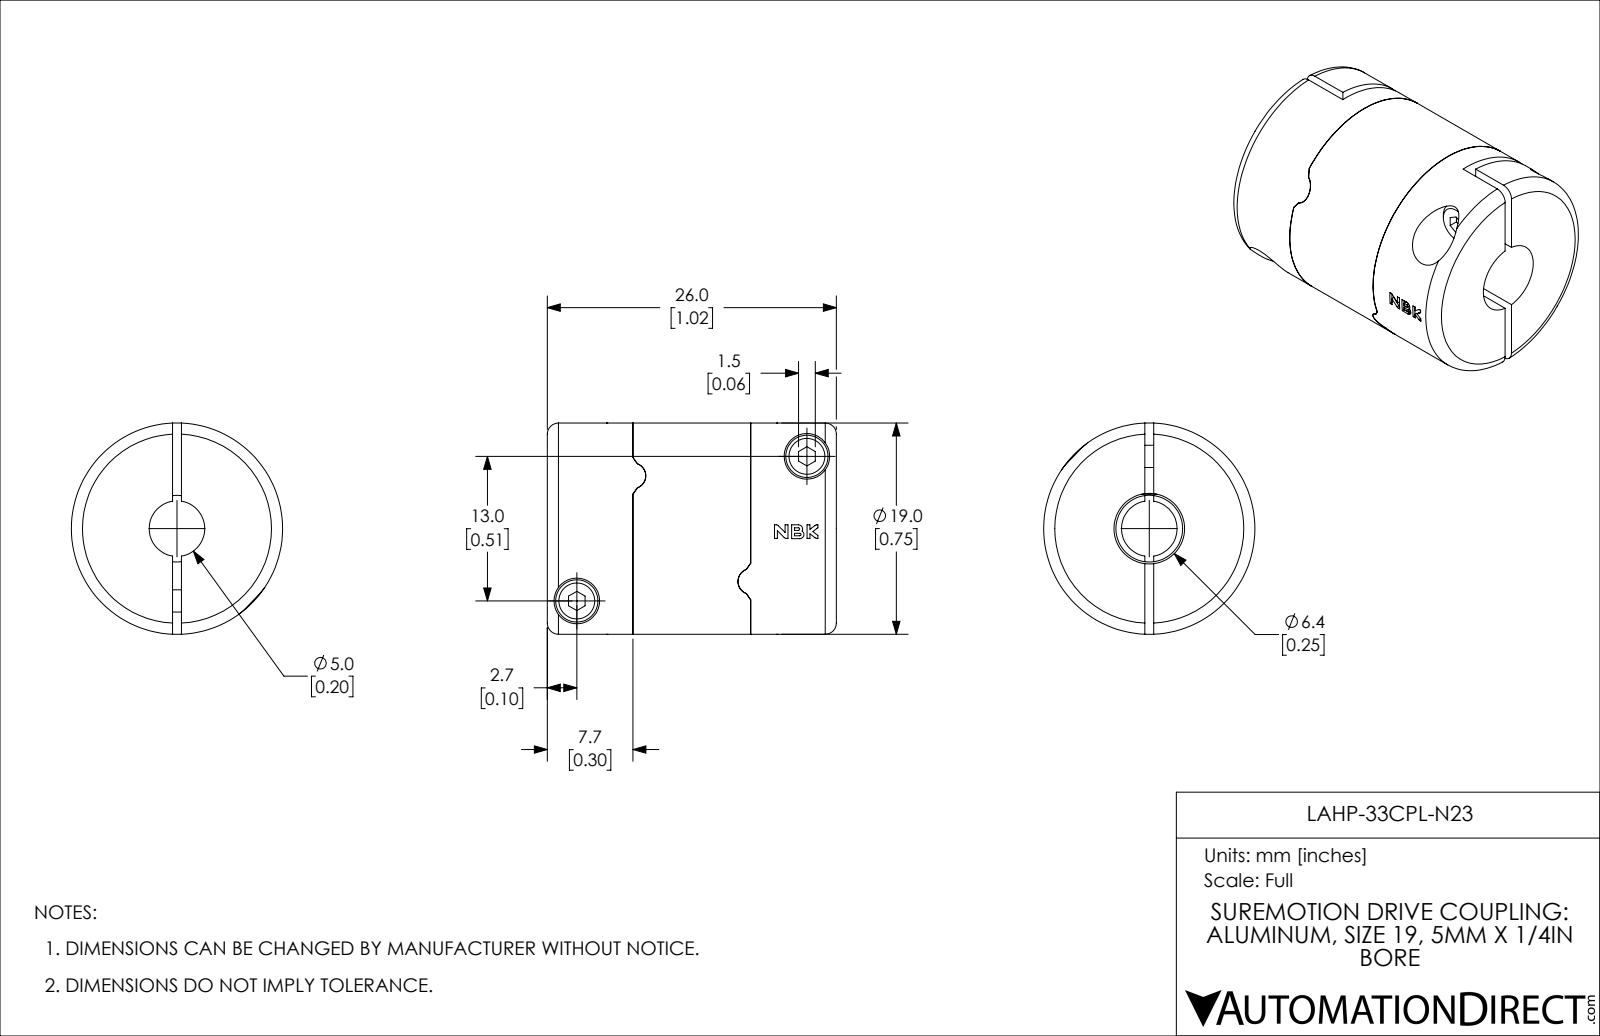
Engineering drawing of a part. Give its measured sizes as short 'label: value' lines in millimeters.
name: LAHP-33CPL-N23
written by: SolidWorks 2019 (CONFIG_CONTROL_DESIGN)
unit: mm
bodies: 3 solids, 166 faces (90 planar, 62 cylindrical, 14 other)
size: 26 × 19 × 19
volume: 6 110 mm³; area: 4 494 mm²
holes: 2× ⌀2, 2× ⌀2.5, 2× ⌀4.1, 1× ⌀5, 1× ⌀6, 1× ⌀6.4, 1× ⌀7
bosses: 2× ⌀3.8, 1× ⌀19
rounds: 4× R0.3, 2× R1.1, 1× R0.1, 1× R0.1, 1× R0.4, 1× R0.4
face distances: 10.6, 7.7, 18.3, 0.8, 5.4, 20.7, 2.4, 13, 4.5, 21.4
hole spacings: 24.4
